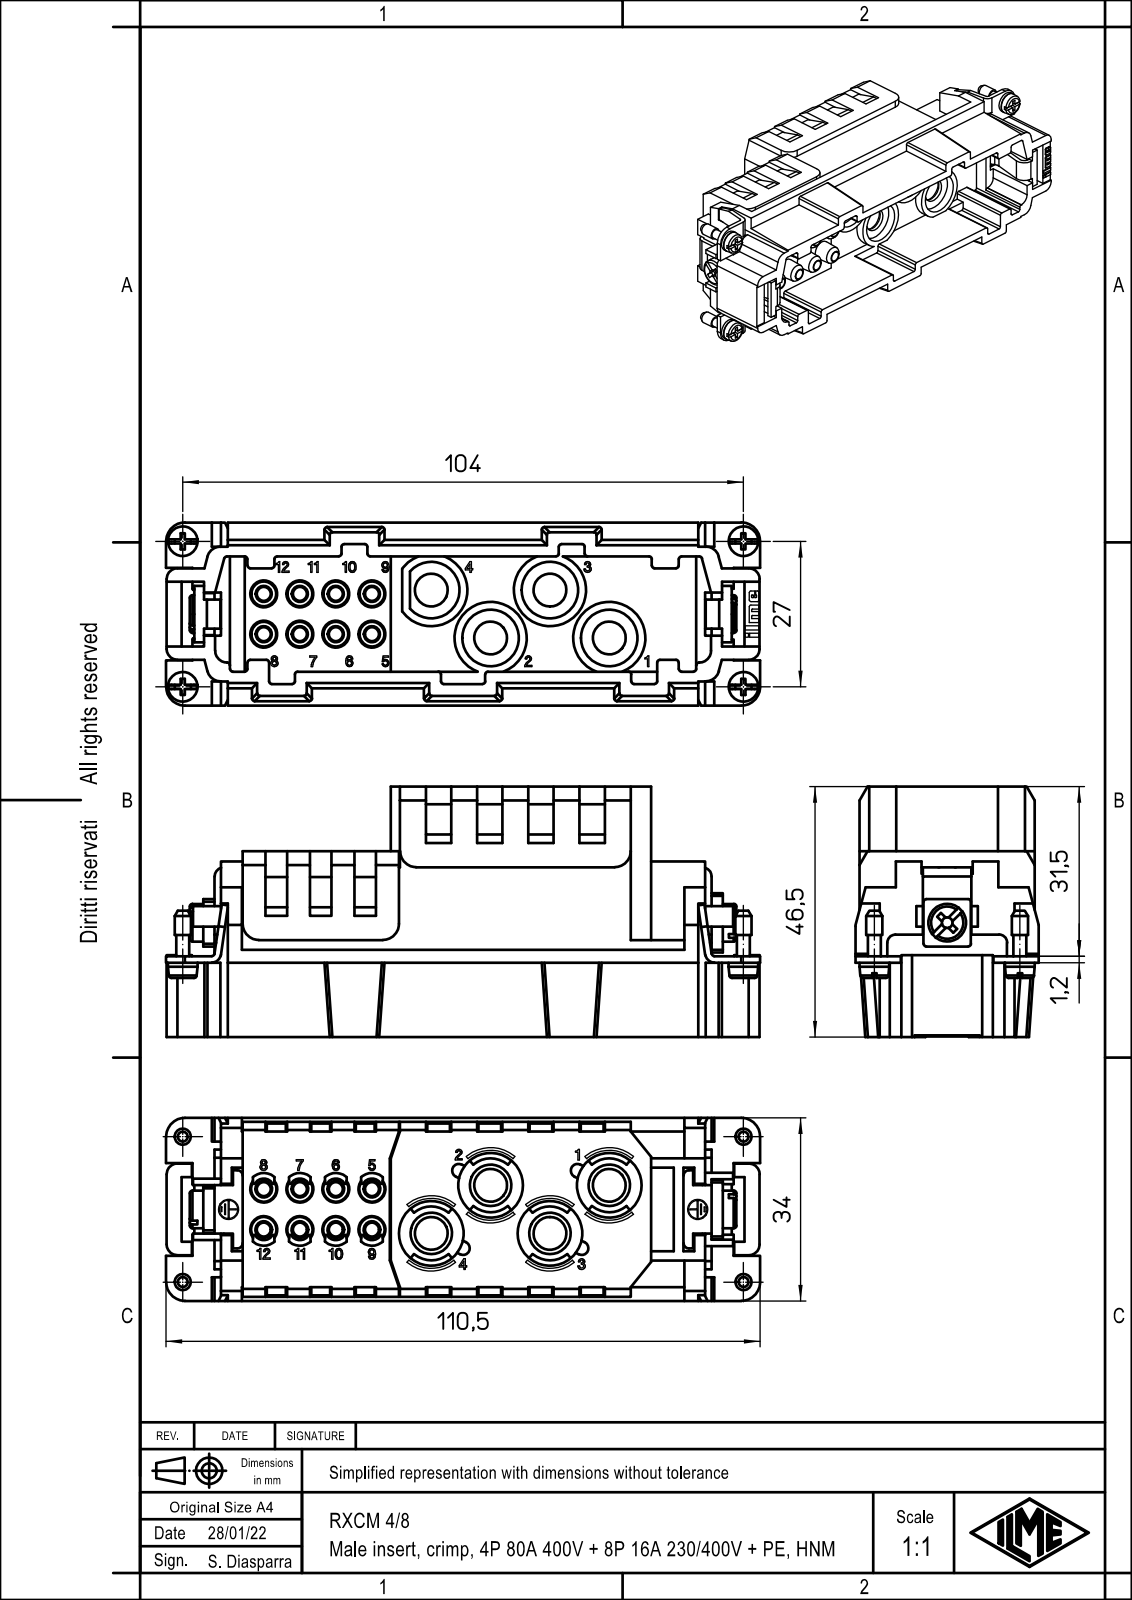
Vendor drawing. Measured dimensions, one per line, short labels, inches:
name: RXCM_4-8
written by: Creo Elements/Direct Modeling 20.1B 02-Apr-2019 (C) Parametric Technology GmbH (AUTOMOTIVE_DESIGN)
unit: in
bodies: 1 solid, 1777 faces (1438 planar, 239 cylindrical, 100 other)
size: 4.339 × 1.831 × 1.339
volume: 4.014 in³; area: 55.24 in²
holes: 8× ⌀0.102, 4× ⌀0.24, 4× ⌀0.472, 3× ⌀0.413, 1× ⌀0.079
bosses: 4× ⌀0.217, 4× ⌀0.118, 4× ⌀0.094, 3× ⌀0.528, 1× ⌀0.276
rounds: 56× R0.02, 14× R0.098, 12× R0.118, 8× R0.077, 6× R0.004, 6× R0.079, 5× R0.012, 4× R0.049
face distances: 0.071, 0.148, 0.99, 0.047, 1.061, 1.28, 0.219, 1.209, 0.157, 0.087
hole spacings: 0.264, 0.396, 0.295, 0.528, 0.605, 0.557, 0.791, 0.844
